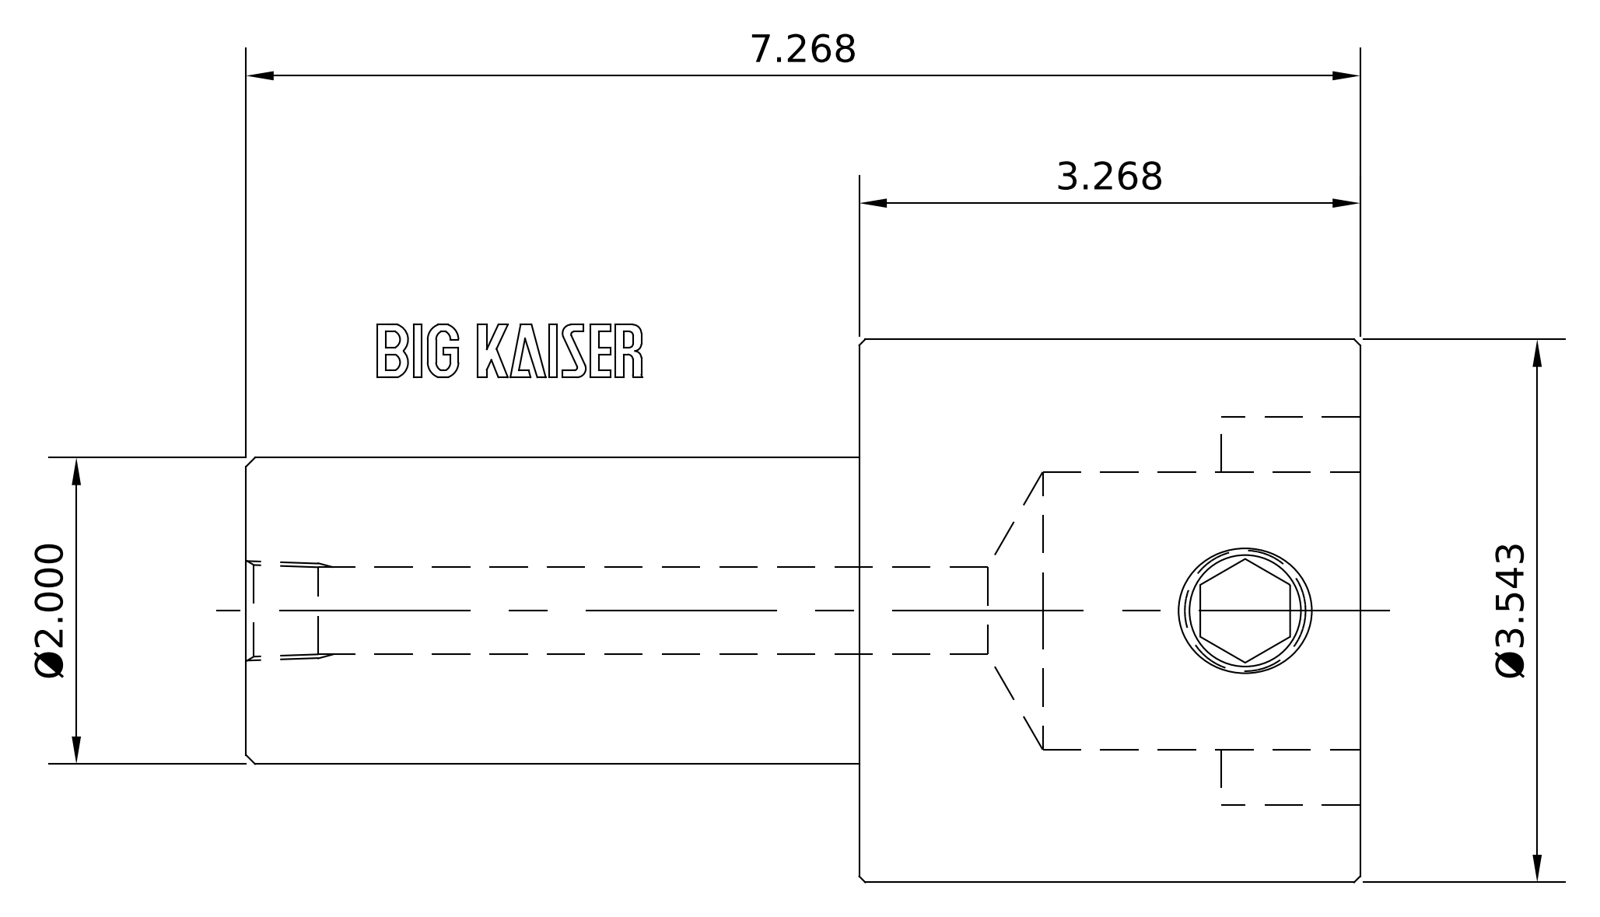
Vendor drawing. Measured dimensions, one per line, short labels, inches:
name: 11.361.474
written by: SolidWorks 2018 (CONFIG_CONTROL_DESIGN)
unit: in
bodies: 1 solid, 52 faces (23 planar, 12 cylindrical, 17 other)
size: 7.268 × 3.543 × 3.543
volume: 34.35 in³; area: 106.7 in²
holes: 2× ⌀0.567, 1× ⌀0.689, 1× ⌀0.827, 1× ⌀1.417, 1× ⌀1.732, 1× ⌀1.811, 1× ⌀1.85
bosses: 1× ⌀3.543, 1× ⌀2
rounds: 2× R0.276
face distances: 3.268, 4, 7.268, 0.759, 5.063, 1.063, 2.205, 1.541, 6.402, 2.402
hole spacings: 1.927
